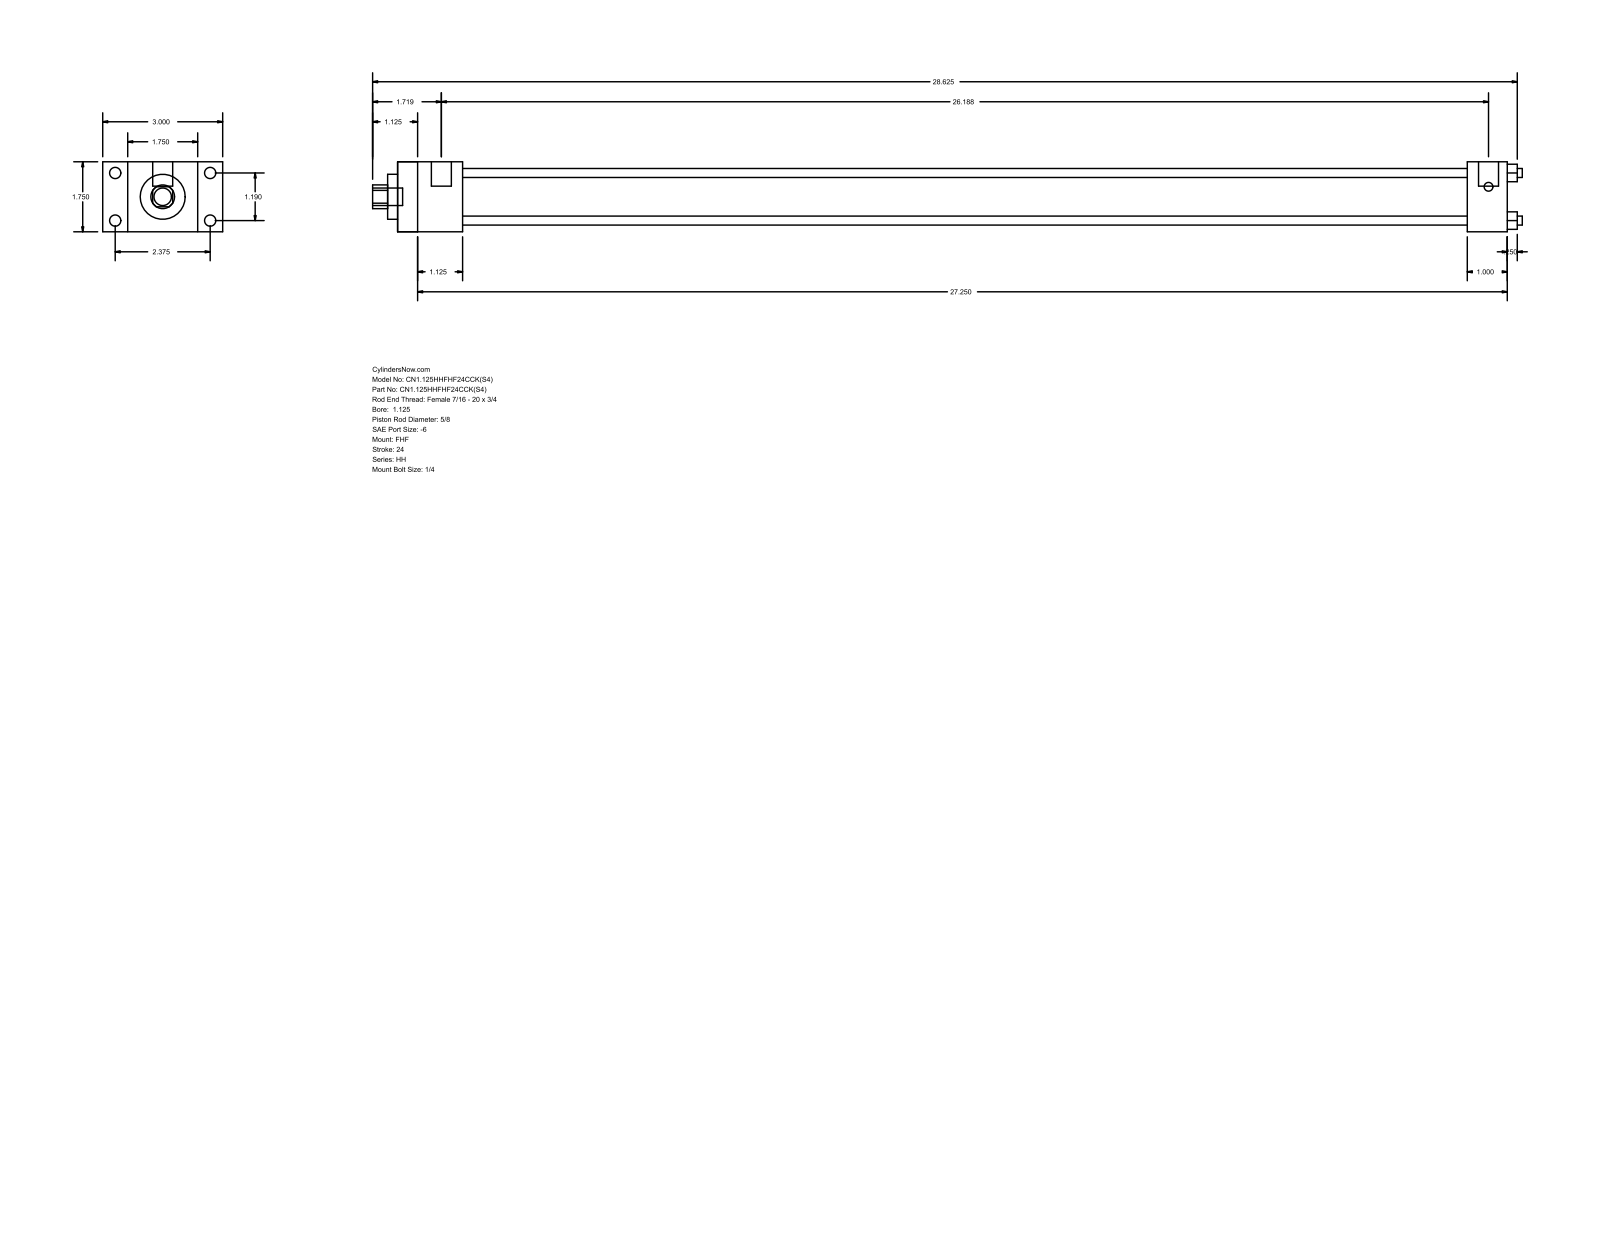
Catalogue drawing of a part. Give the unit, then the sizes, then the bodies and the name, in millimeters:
Units: millimetres
Overall size (bounding box): 730.25 × 76.2 × 44.45
Round holes (diameter × count): ⌀5.71 ×4, ⌀15.88 ×1, ⌀28.57 ×1, ⌀34.92 ×1
Round bosses / shafts (diameter × count): ⌀7.14 ×4, ⌀5.56 ×4, ⌀12.7 ×2, ⌀11.11 ×1
Partial cylindrical surfaces — rounded edges, fillets, slot ends (radius × count): R7.54 ×1
Main face-to-face distances: 44.46, 15.87, 60.33, 41.27, 76.2, 704.85, 663.58, 679.45, 638.18, 25.4
Hole centre spacings: 21.37, 30.22, 42.74
Bodies: 0 solids, 88 faces (60 planar, 28 cylindrical, 0 other)
Part name (STEP PRODUCT): HH_FHF__0112_0.625
STEP written by: GSSL Pune (CONFIG_CONTROL_DESIGN)
